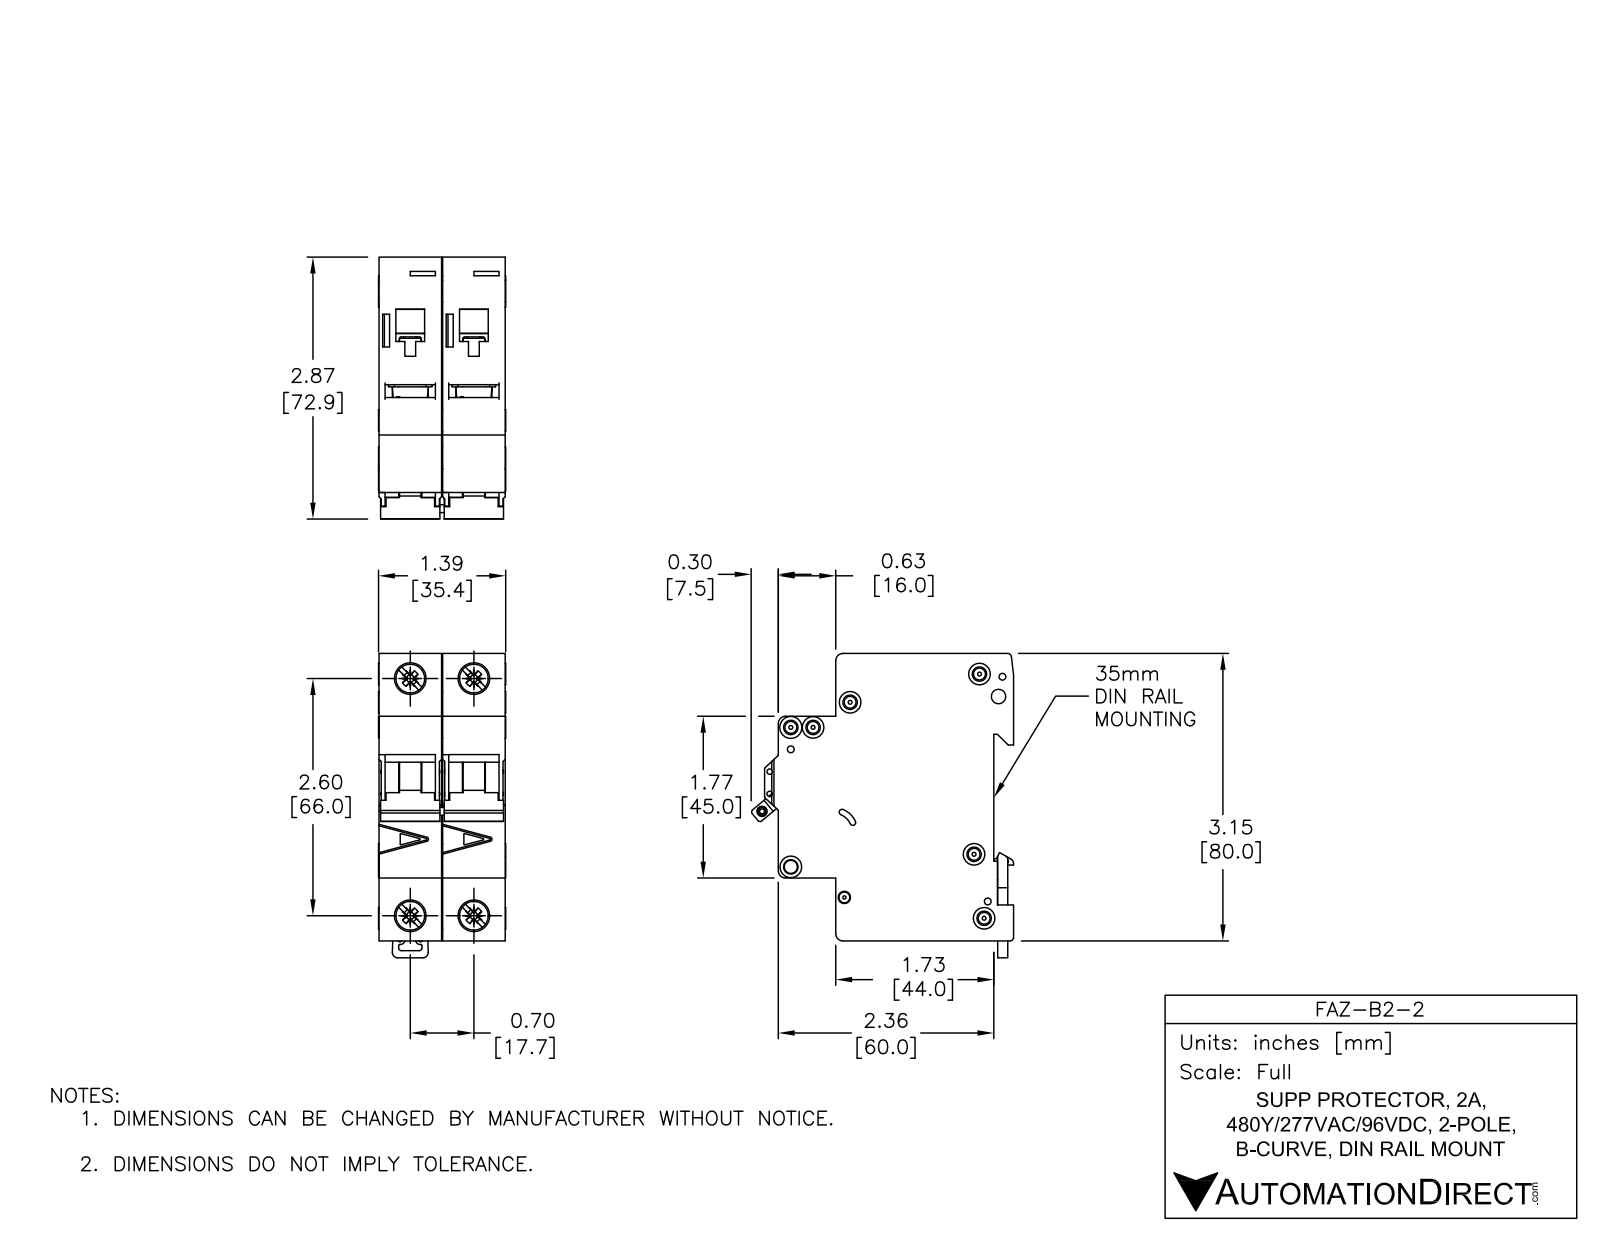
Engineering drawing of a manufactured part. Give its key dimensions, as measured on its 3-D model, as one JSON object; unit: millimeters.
{"part_name": "FAZ-B2-2", "step_written_by": "SolidWorks 2014 (AUTOMOTIVE_DESIGN)", "units": "millimeters", "bodies": {"solids": 8, "faces": 1104, "planar": 466, "cylindrical": 396, "other": 242}, "overall_size": [84.78, 73.04, 35.4], "volume_mm3": 149808, "surface_area_mm2": 38799, "round_holes": [[3.6, 6], [1.9, 3], [1.09, 2], [1.5, 2], [4, 2], [7.15, 2], [8.2, 2], [2.15, 1], [2.2, 1], [2.55, 1], [3.3, 1], [3.4, 1]], "round_bosses_or_shafts": [[6, 4], [8.2, 2], [2.5, 2]], "partial_cylinders_radius": [[0.25, 49], [0.5, 19], [2, 10], [0.2, 8], [1, 8], [0.8, 2], [1.8, 2], [3, 2]], "face_to_face_distances": [17.7, 17.5, 35.2, 79.48, 5.5, 49.5, 44, 65.5, 60, 16], "hole_center_spacings": [6.2, 13.64, 17.7, 66, 68.33, 4.81, 5.19, 5.61]}
